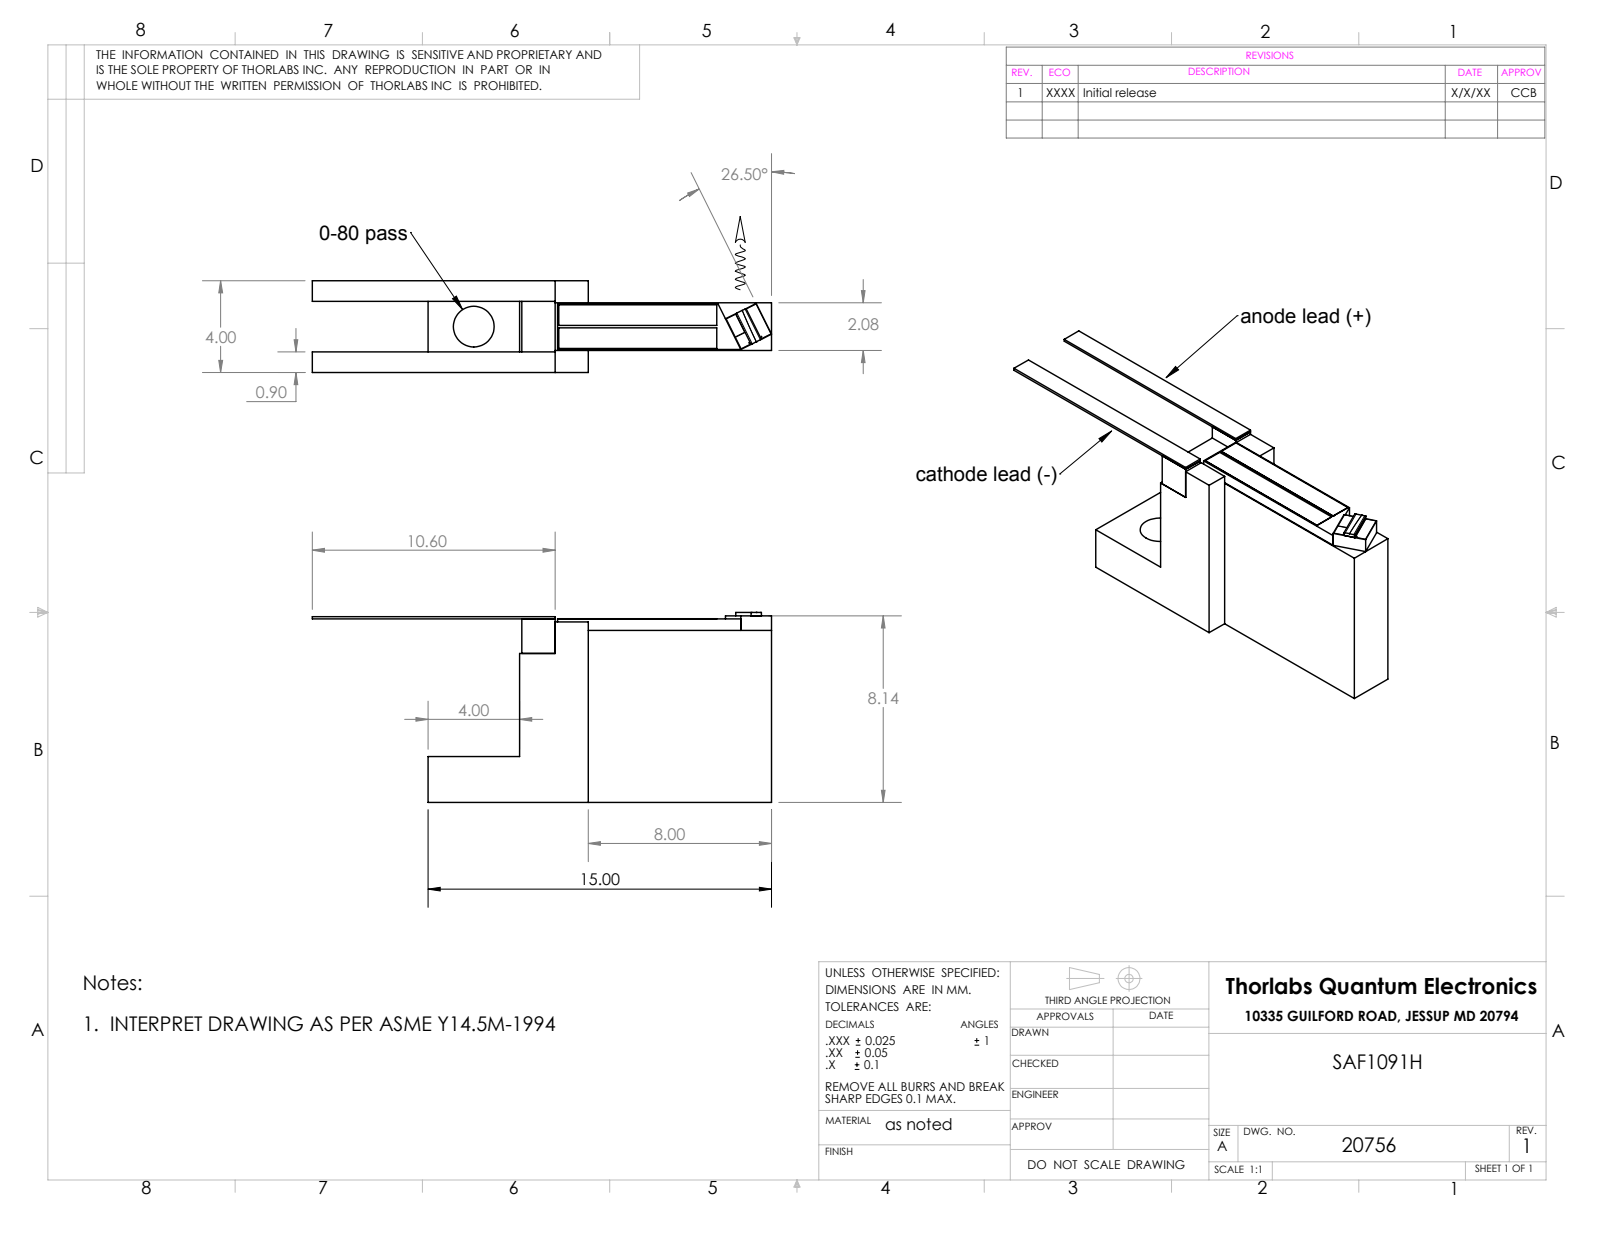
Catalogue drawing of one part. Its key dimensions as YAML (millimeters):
part_name: "PA-00137; PM-00054; 31091-XXX; 22292-XXX (+5 more)"
step_written_by: "SolidWorks 2009 (CONFIG_CONTROL_DESIGN)"
units: millimeters
bodies: {solids: 7, faces: 84, planar: 82, cylindrical: 2, other: 0}
overall_size: [20.05, 8.29, 4]
volume: 255
surface_area: 457
round_holes:
  - {diameter: 1.78, count: 1}
face_to_face_distances: [0.96, 3.04, 2.08, 4, 8, 7.5, 0.5, 3, 0.6, 1]
